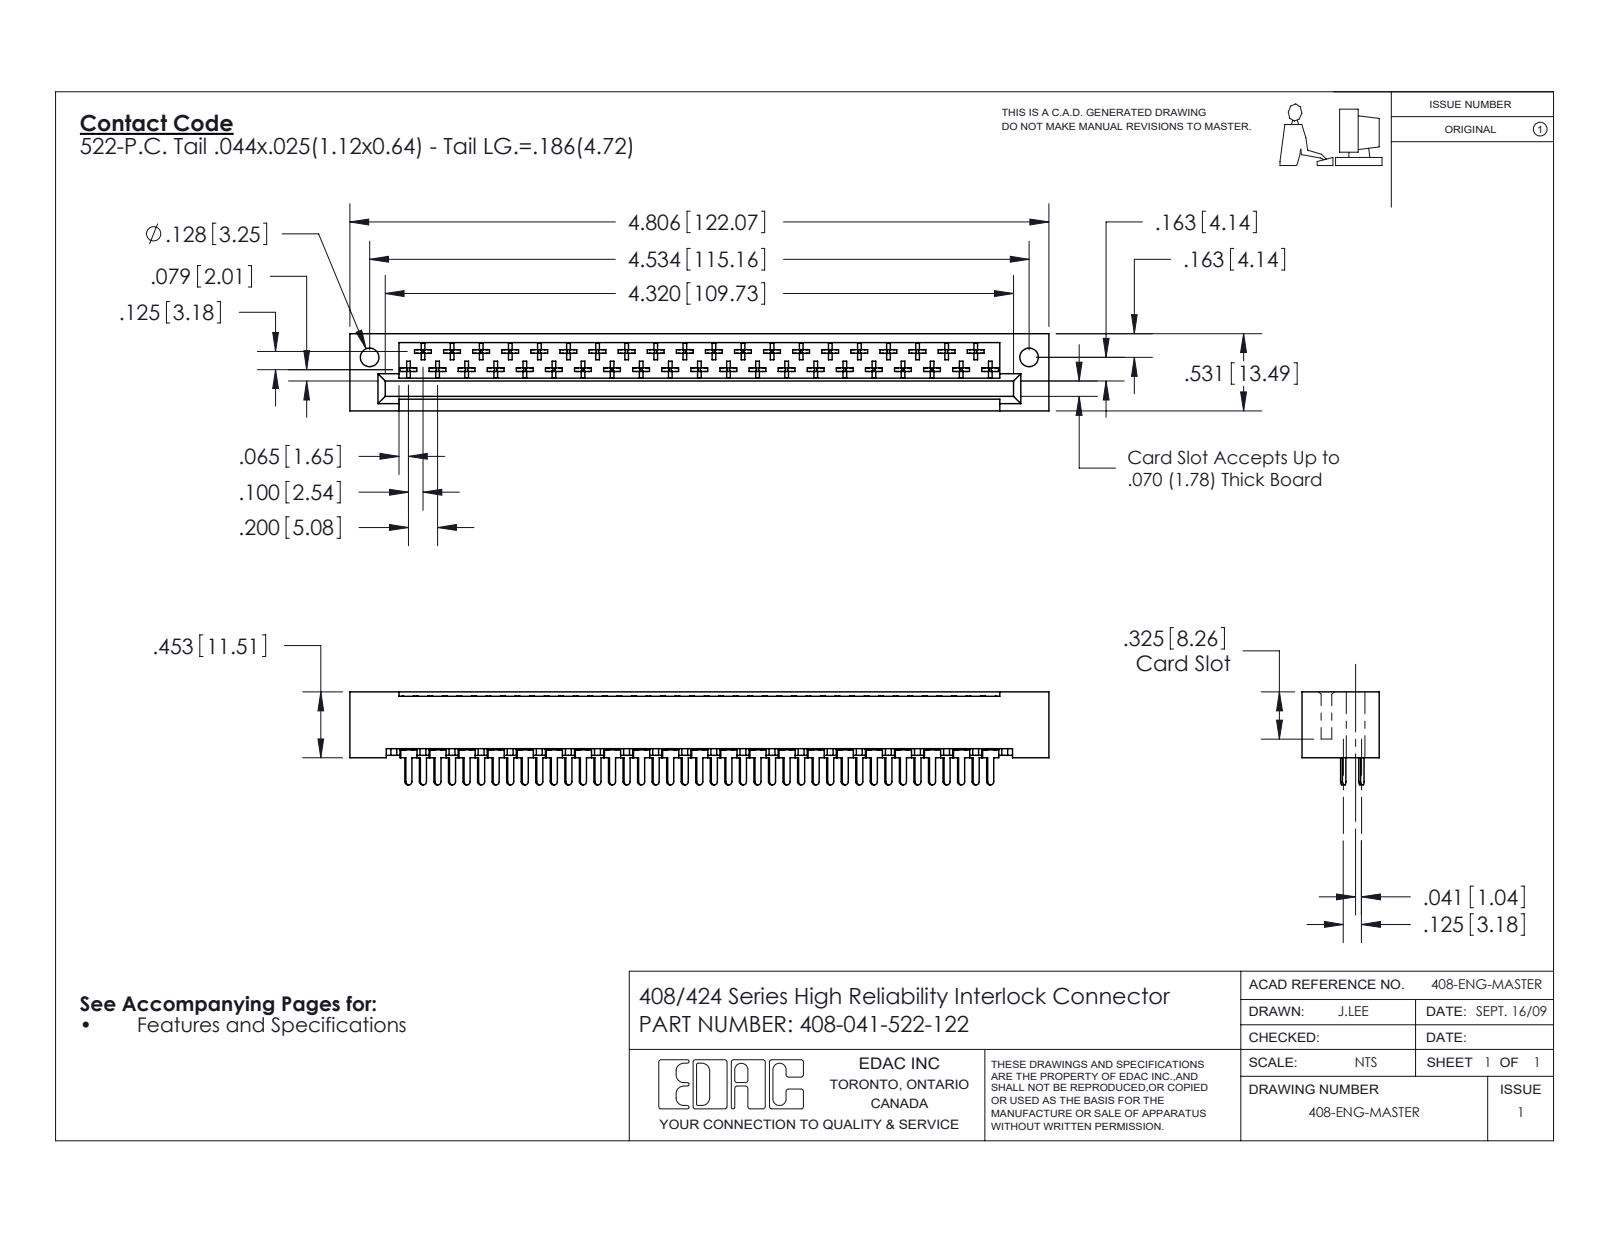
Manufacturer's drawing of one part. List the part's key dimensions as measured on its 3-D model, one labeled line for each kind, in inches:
Part name (STEP PRODUCT): 408 Part_041 - 1; 408-047-522-122; 408-290-001_408-290-122
STEP written by: SolidWorks 2016 (CONFIG_CONTROL_DESIGN)
Units: inches
Bodies: 42 solids, 2299 faces (1758 planar, 377 cylindrical, 164 other)
Overall size (bounding box): 4.806 × 0.639 × 0.531
Volume: 0.812 in³ · Surface area: 26.08 in²
Round holes (diameter × count): ⌀0.128 ×2
Partial cylindrical surfaces — rounded edges, fillets, slot ends (radius × count): R0.01 ×246, R0.02 ×43, R0.022 ×41
Main face-to-face distances: 0.1, 0.296, 0.531, 0.125, 0.025, 0.025, 0.259, 0.272, 0.235, 0.135
Hole centre spacings: 4.534
